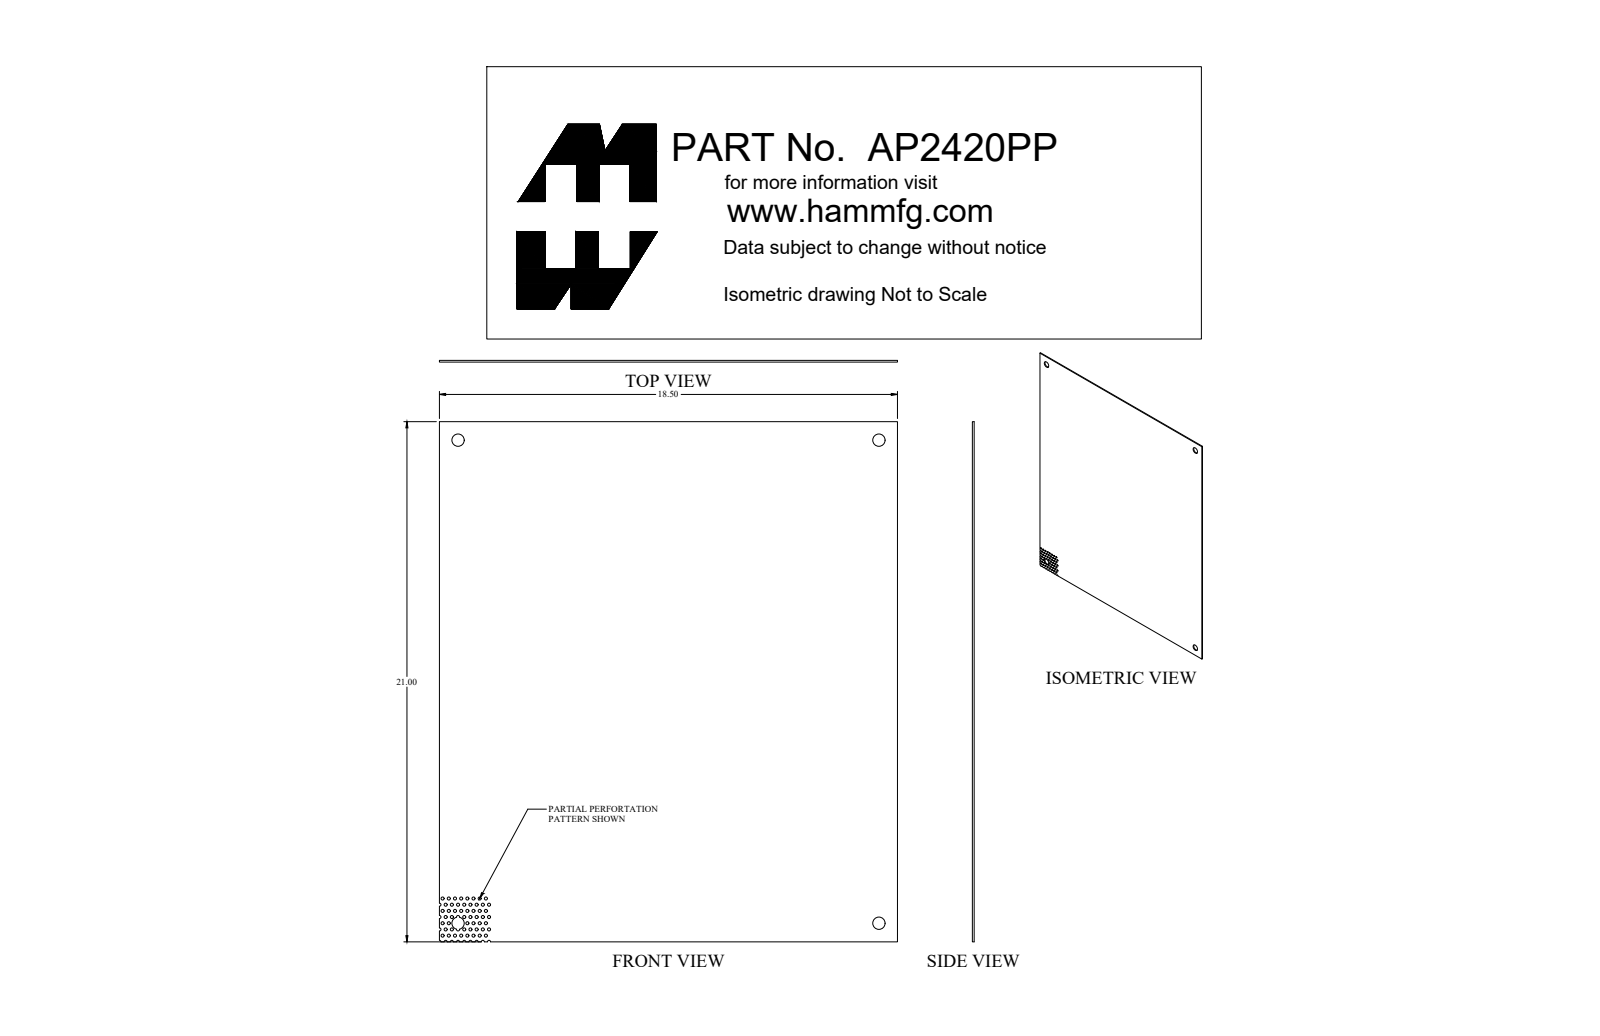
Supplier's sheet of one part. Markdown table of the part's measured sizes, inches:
| quantity | value |
| --- | --- |
| part name | AP2420PP_Default |
| STEP written by | SolidWorks 2019 (CONFIG_CONTROL_DESIGN) |
| units | inches |
| bodies | 1 solid, 152 faces (17 planar, 135 cylindrical, 0 other) |
| overall size | 21 × 18.5 × 0.072 |
| volume | 27.86 in³ |
| surface area | 781.7 in² |
| round holes (diameter × count) | 0.125 × 37, 0.125 × 15, 0.5 × 4 |
| partial cylindrical surfaces (radius × count) | 0.063 × 11, 0.062 × 3 |
| main face-to-face distances | 0.072, 18.5, 21 |
| hole center spacings | 0.28, 0.5, 0.559, 0.25, 0.451, 1.152, 0.707, 0.76 |
